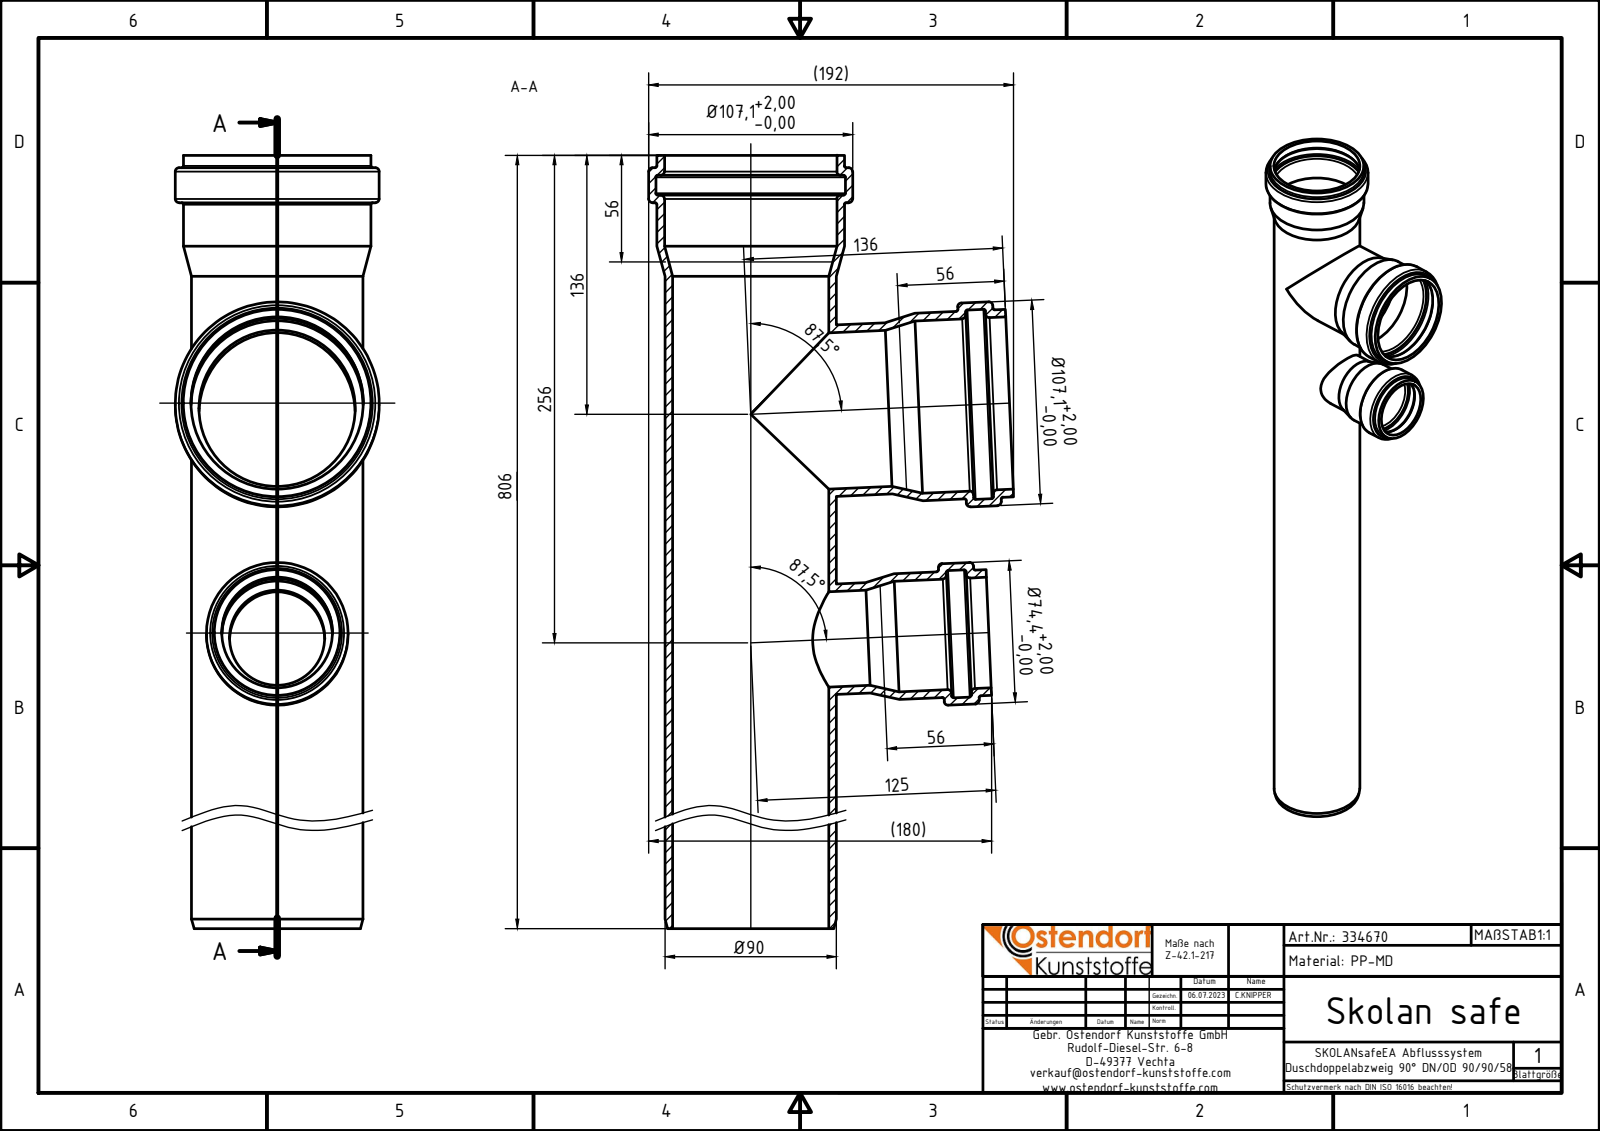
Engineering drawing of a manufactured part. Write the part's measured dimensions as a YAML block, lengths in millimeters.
part_name: "334670 SKOLANsafe Duschdoppelabzweig DN_OD 90_90_58"
step_written_by: "Autodesk Inventor 2016 (AUTOMOTIVE_DESIGN)"
units: millimeters
bodies: {solids: 1, faces: 71, planar: 16, cylindrical: 24, other: 31}
overall_size: [806, 191.57, 107.1]
volume: 1053000
surface_area: 529883
round_holes:
  - {diameter: 90.5, count: 3}
  - {diameter: 58.1, count: 2}
  - {diameter: 82, count: 2}
  - {diameter: 99.5, count: 2}
  - {diameter: 50, count: 1}
  - {diameter: 66.8, count: 1}
round_bosses_or_shafts:
  - {diameter: 98.5, count: 3}
  - {diameter: 107.1, count: 2}
  - {diameter: 90, count: 2}
  - {diameter: 66.1, count: 2}
  - {diameter: 74.4, count: 1}
  - {diameter: 58, count: 1}
face_to_face_distances: [4, 14.4, 16.15, 10.5, 10.4, 20.9, 24.9, 18.4, 6.5, 806]
hole_center_spacings: [119.88, 119.89, 119.85, 119.86, 119.87, 119.91, 119.92]
